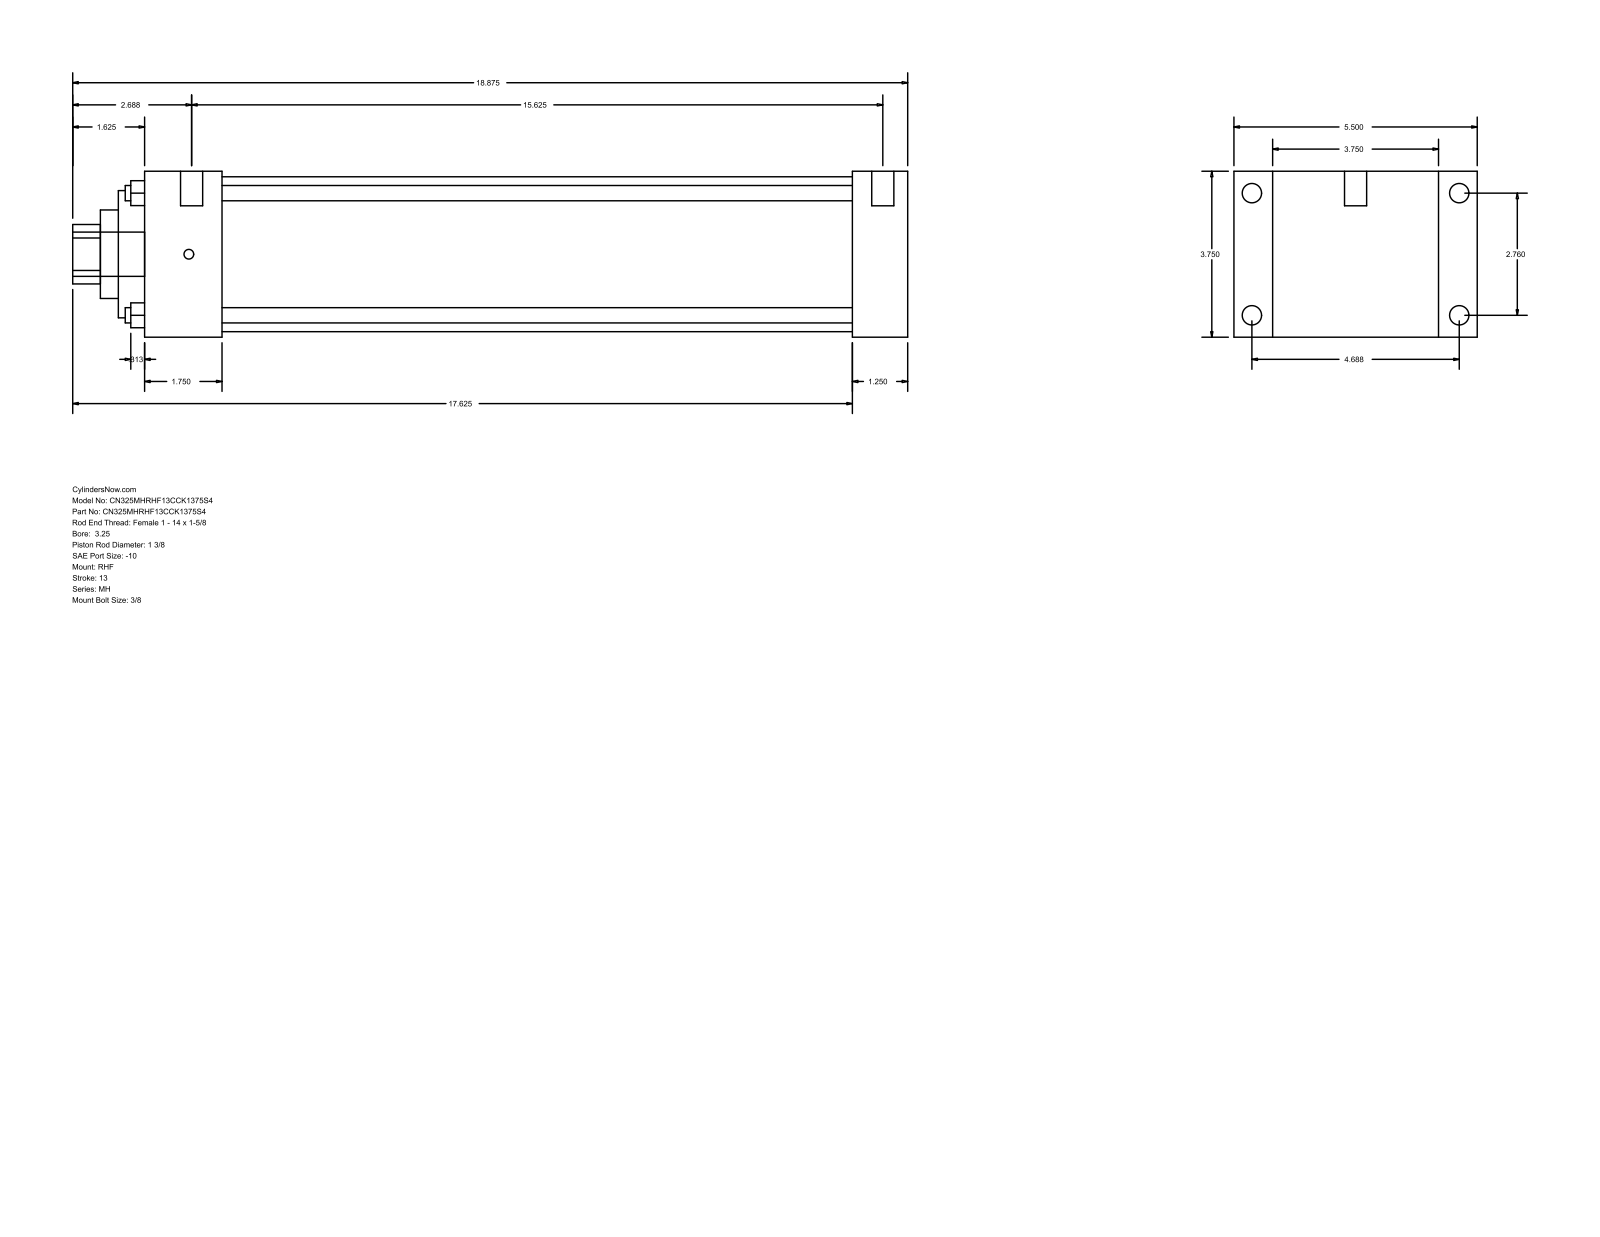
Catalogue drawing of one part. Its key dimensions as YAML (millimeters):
part_name: "MH_RHF__0325_1.375"
step_written_by: "GSSL Pune (CONFIG_CONTROL_DESIGN)"
units: millimeters
bodies: {solids: 0, faces: 90, planar: 61, cylindrical: 29, other: 0}
overall_size: [479.43, 139.7, 95.25]
round_holes:
  - {diameter: 8.76, count: 4}
  - {diameter: 34.92, count: 1}
  - {diameter: 50.8, count: 1}
  - {diameter: 73.03, count: 1}
  - {diameter: 88.9, count: 1}
round_bosses_or_shafts:
  - {diameter: 11.13, count: 4}
  - {diameter: 5.56, count: 4}
  - {diameter: 12.7, count: 2}
  - {diameter: 25.4, count: 1}
partial_cylinders:
  - {radius: 17.06, count: 1}
face_to_face_distances: [95.24, 31.75, 22.23, 117.47, 406.41, 438.16, 139.7, 44.45, 361.96, 393.71]
hole_center_spacings: [49.57, 70.1, 99.14]
